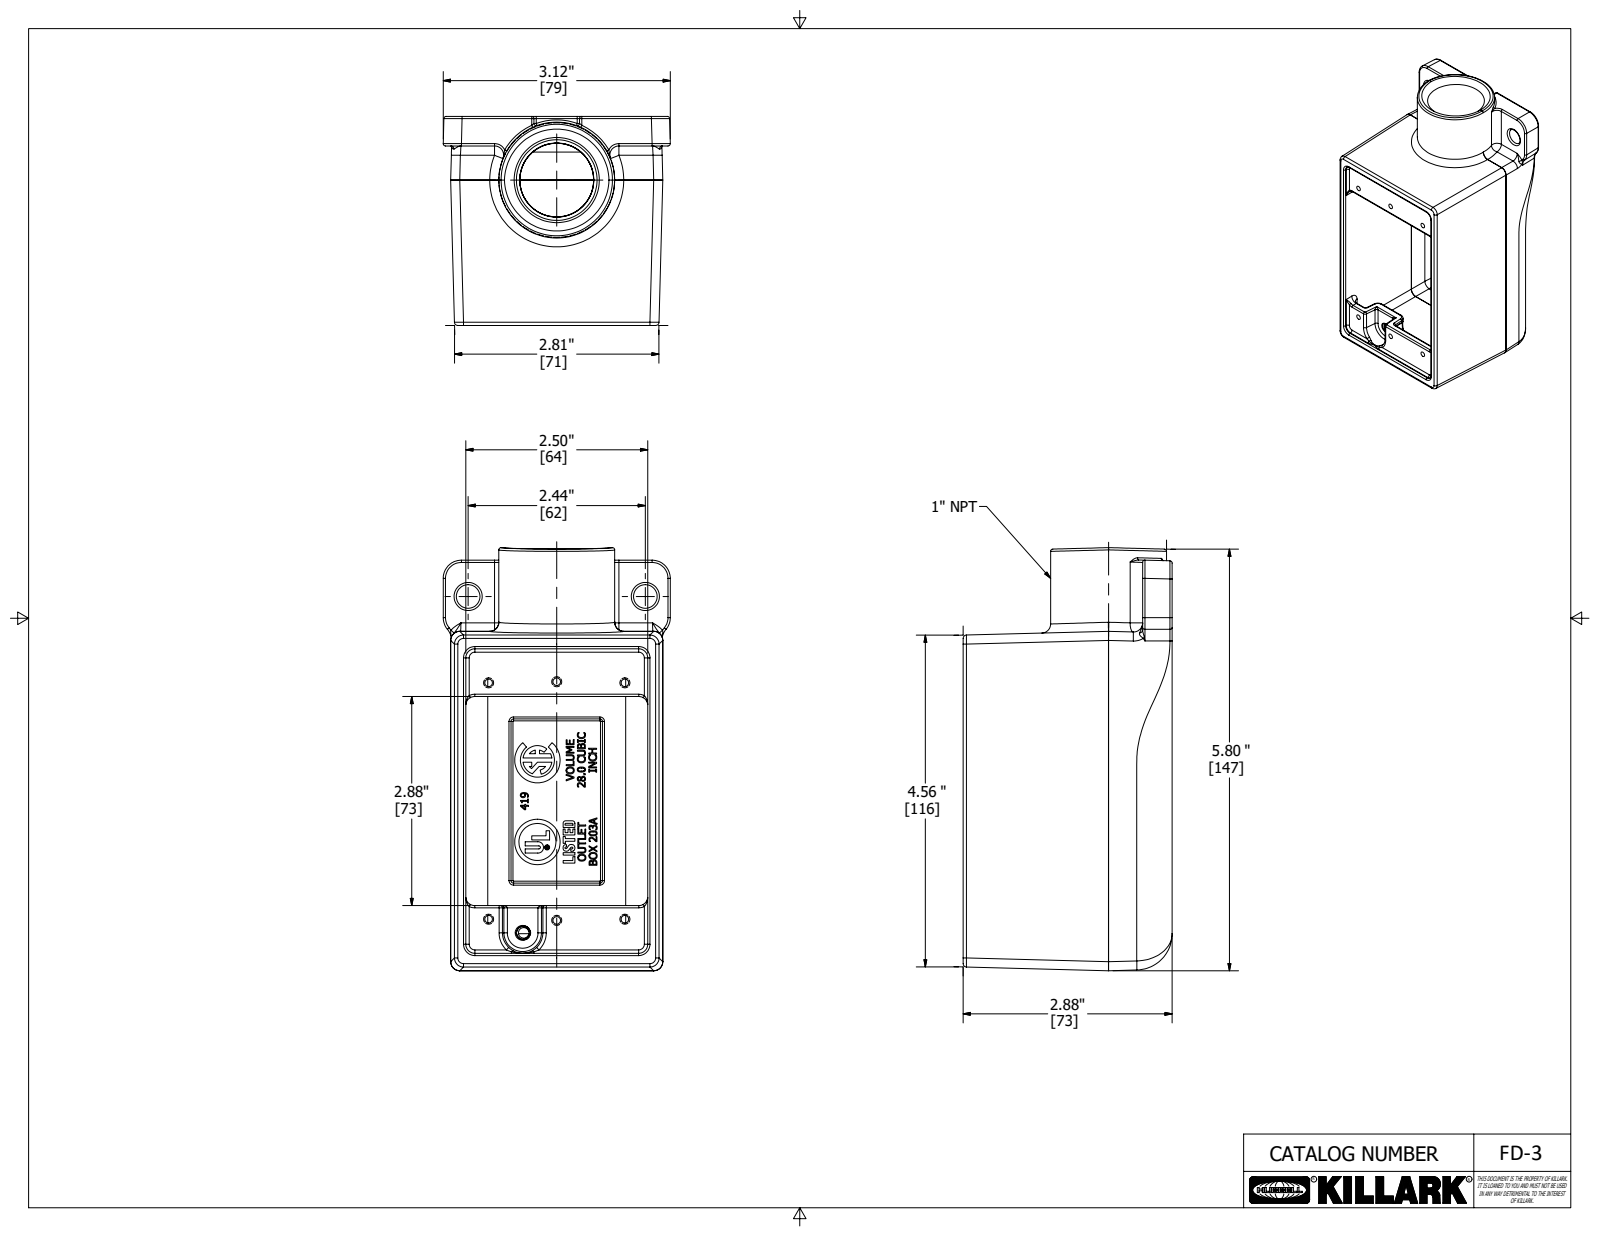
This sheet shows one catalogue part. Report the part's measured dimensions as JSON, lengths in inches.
{"part_name": "23642-3", "step_written_by": "Autodesk Inventor 2020 (AUTOMOTIVE_DESIGN)", "units": "inches", "bodies": {"solids": 1, "faces": 1184, "planar": 558, "cylindrical": 185, "other": 441}, "overall_size": [5.818, 3.123, 2.875], "volume_in3": 10.5, "surface_area_in2": 121.6, "round_holes": [[0.104, 6], [0.069, 1], [0.145, 1], [0.625, 1]], "round_bosses_or_shafts": [[1.594, 1], [0.509, 1], [0.058, 1]], "partial_cylinders_radius": [[0.031, 53], [0.125, 38], [0.047, 12], [0.25, 6], [0.344, 4], [0.013, 2], [0.014, 2], [0.034, 2]], "face_to_face_distances": [0.156, 2.761, 0.156, 2.917, 2.604, 2.594, 2.469, 4.51, 2.781, 2.625], "hole_center_spacings": [0.937, 3.397, 1.875, 3.25, 3.752, 0.153, 0.486, 0.518]}
